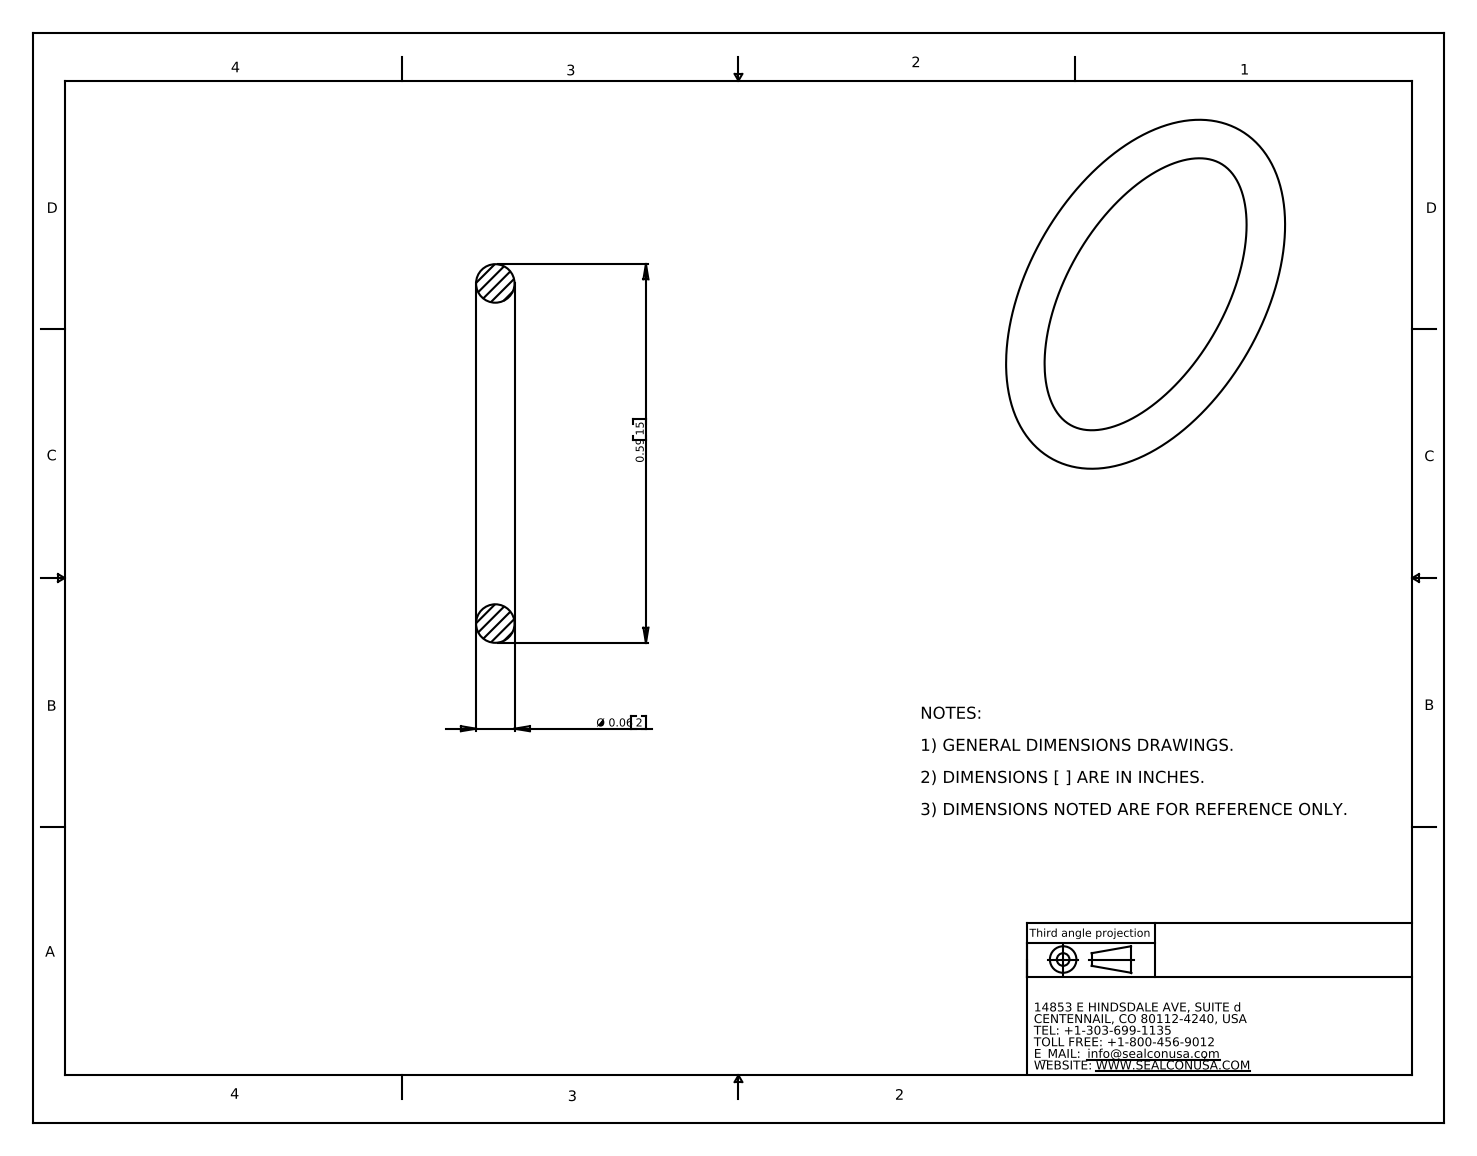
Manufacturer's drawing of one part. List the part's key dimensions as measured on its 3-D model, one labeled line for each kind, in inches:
Part name (STEP PRODUCT): OM-16-VT
STEP written by: SolidWorks 2007 (CONFIG_CONTROL_DESIGN)
Units: inches
Bodies: 1 solid, 4 faces (0 planar, 0 cylindrical, 4 other)
Overall size (bounding box): 0.59 × 0.59 × 0.06
Volume: 0.005 in³ · Surface area: 0.314 in²
